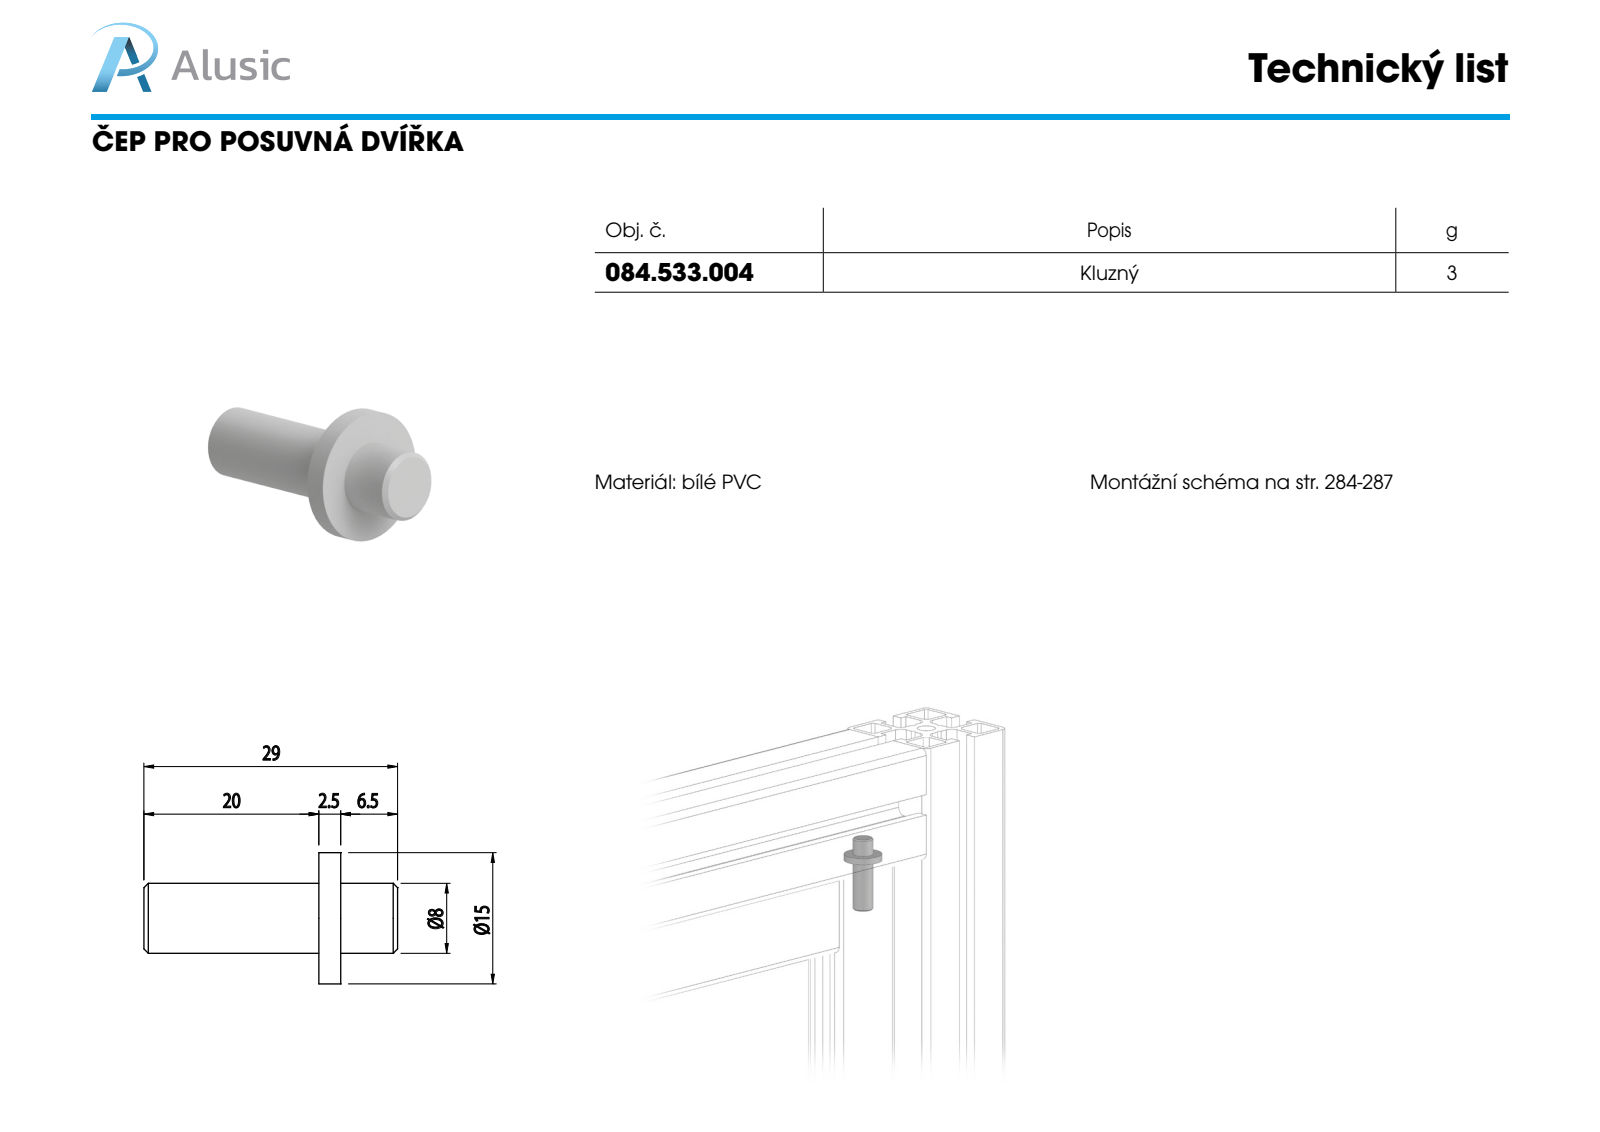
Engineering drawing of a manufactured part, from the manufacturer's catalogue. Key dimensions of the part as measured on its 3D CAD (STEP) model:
Part name (STEP PRODUCT): 084.533.004
STEP written by: SolidWorks 2011 (CONFIG_CONTROL_DESIGN)
Units: millimetres
Bodies: 1 solid, 14 faces (4 planar, 6 cylindrical, 4 other)
Overall size (bounding box): 29 × 15 × 15
Volume: 1 768 mm³ · Surface area: 1 122 mm²
Round bosses / shafts (diameter × count): ⌀15 ×1, ⌀8 ×1
Main face-to-face distances: 2.5, 9, 6.5, 20, 22.5, 29
